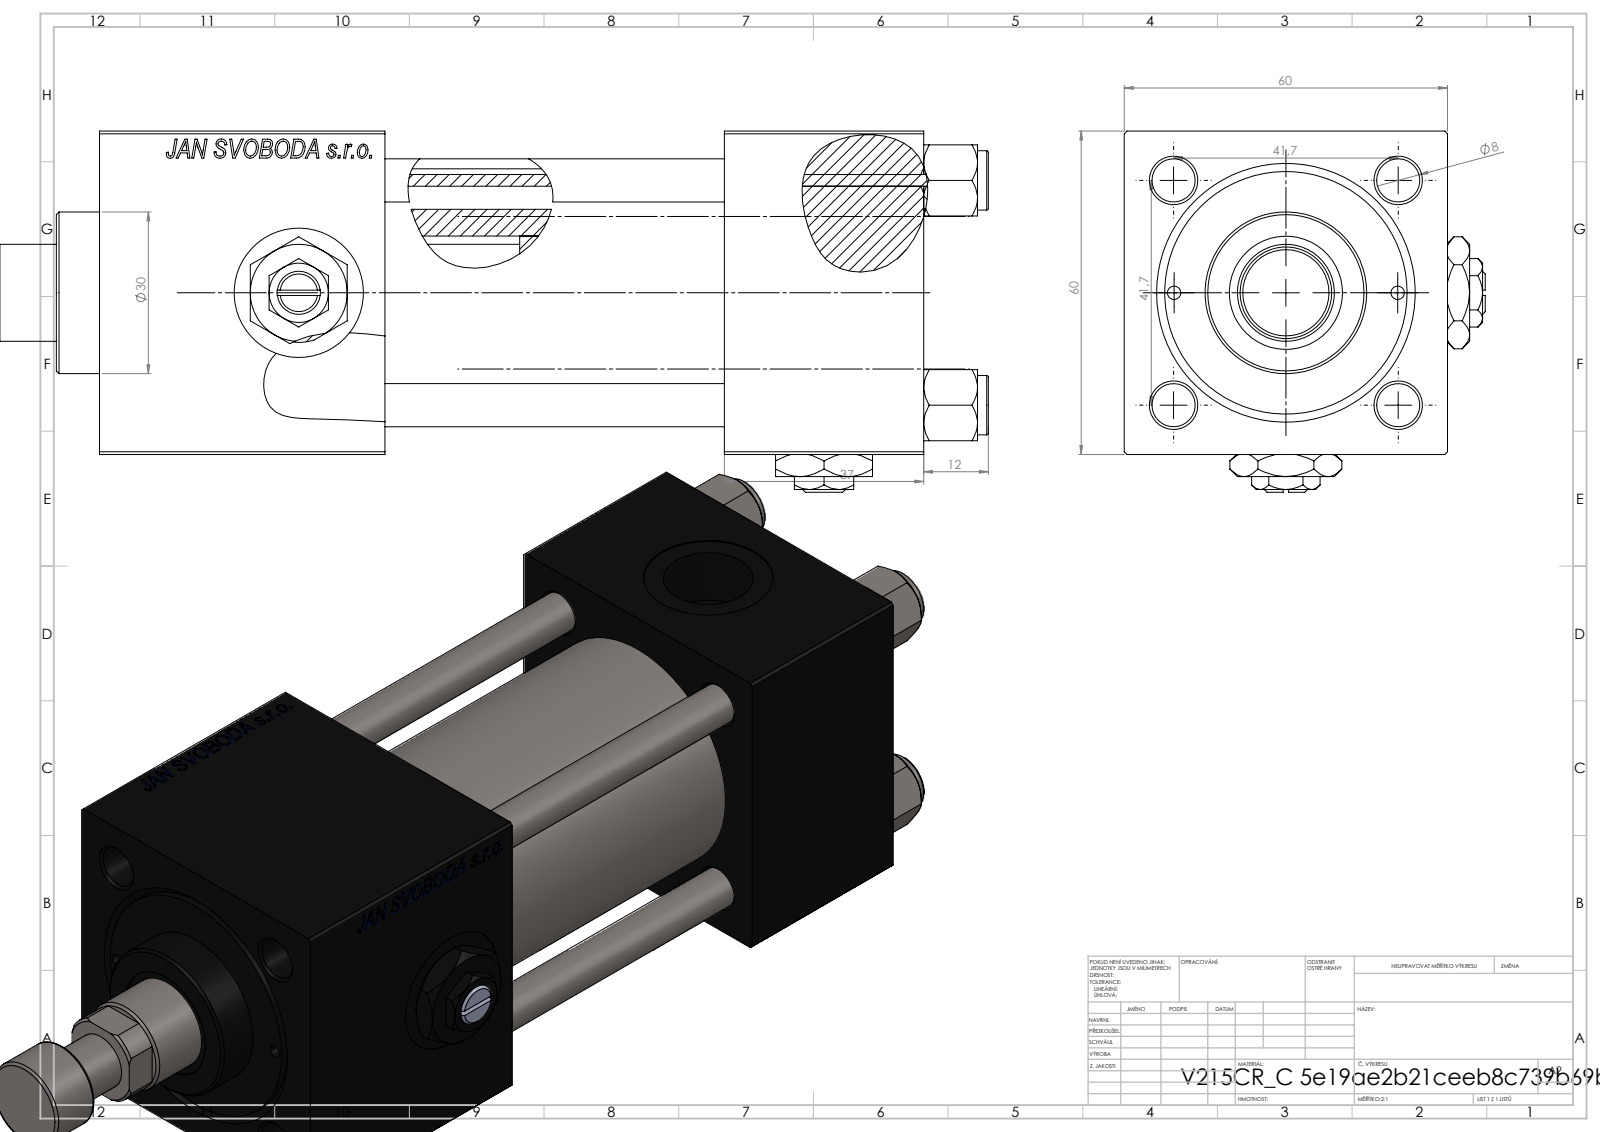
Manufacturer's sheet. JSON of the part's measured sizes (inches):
{"part_name": "Zatka_pro_OIL_PORT; V215CR_VCP_C; V215CR_ROD_END_F; V215_VC_A (+3 more)", "step_written_by": "SolidWorks 2019 (CONFIG_CONTROL_DESIGN)", "units": "inches", "bodies": {"solids": 14, "faces": 1267, "planar": 579, "cylindrical": 106, "other": 582}, "overall_size": [8.268, 2.638, 2.638], "volume_in3": 24.79, "surface_area_in2": 173.4, "round_holes": [[0.315, 4], [0.098, 2], [0.276, 2], [0.656, 2], [0.945, 2], [0.335, 1], [0.709, 1], [0.827, 1], [1.22, 1], [1.575, 1], [1.772, 1]], "round_bosses_or_shafts": [[0.433, 5], [1.811, 1], [1.181, 1], [0.669, 1]], "face_to_face_distances": [2.362, 1.457, 2.48, 6.024, 4.567, 2.087, 3.937, 4.894, 3.437, 0.957], "hole_center_spacings": [0.821, 1.161, 1.642, 1.832, 0.817, 2.322, 1.634]}
